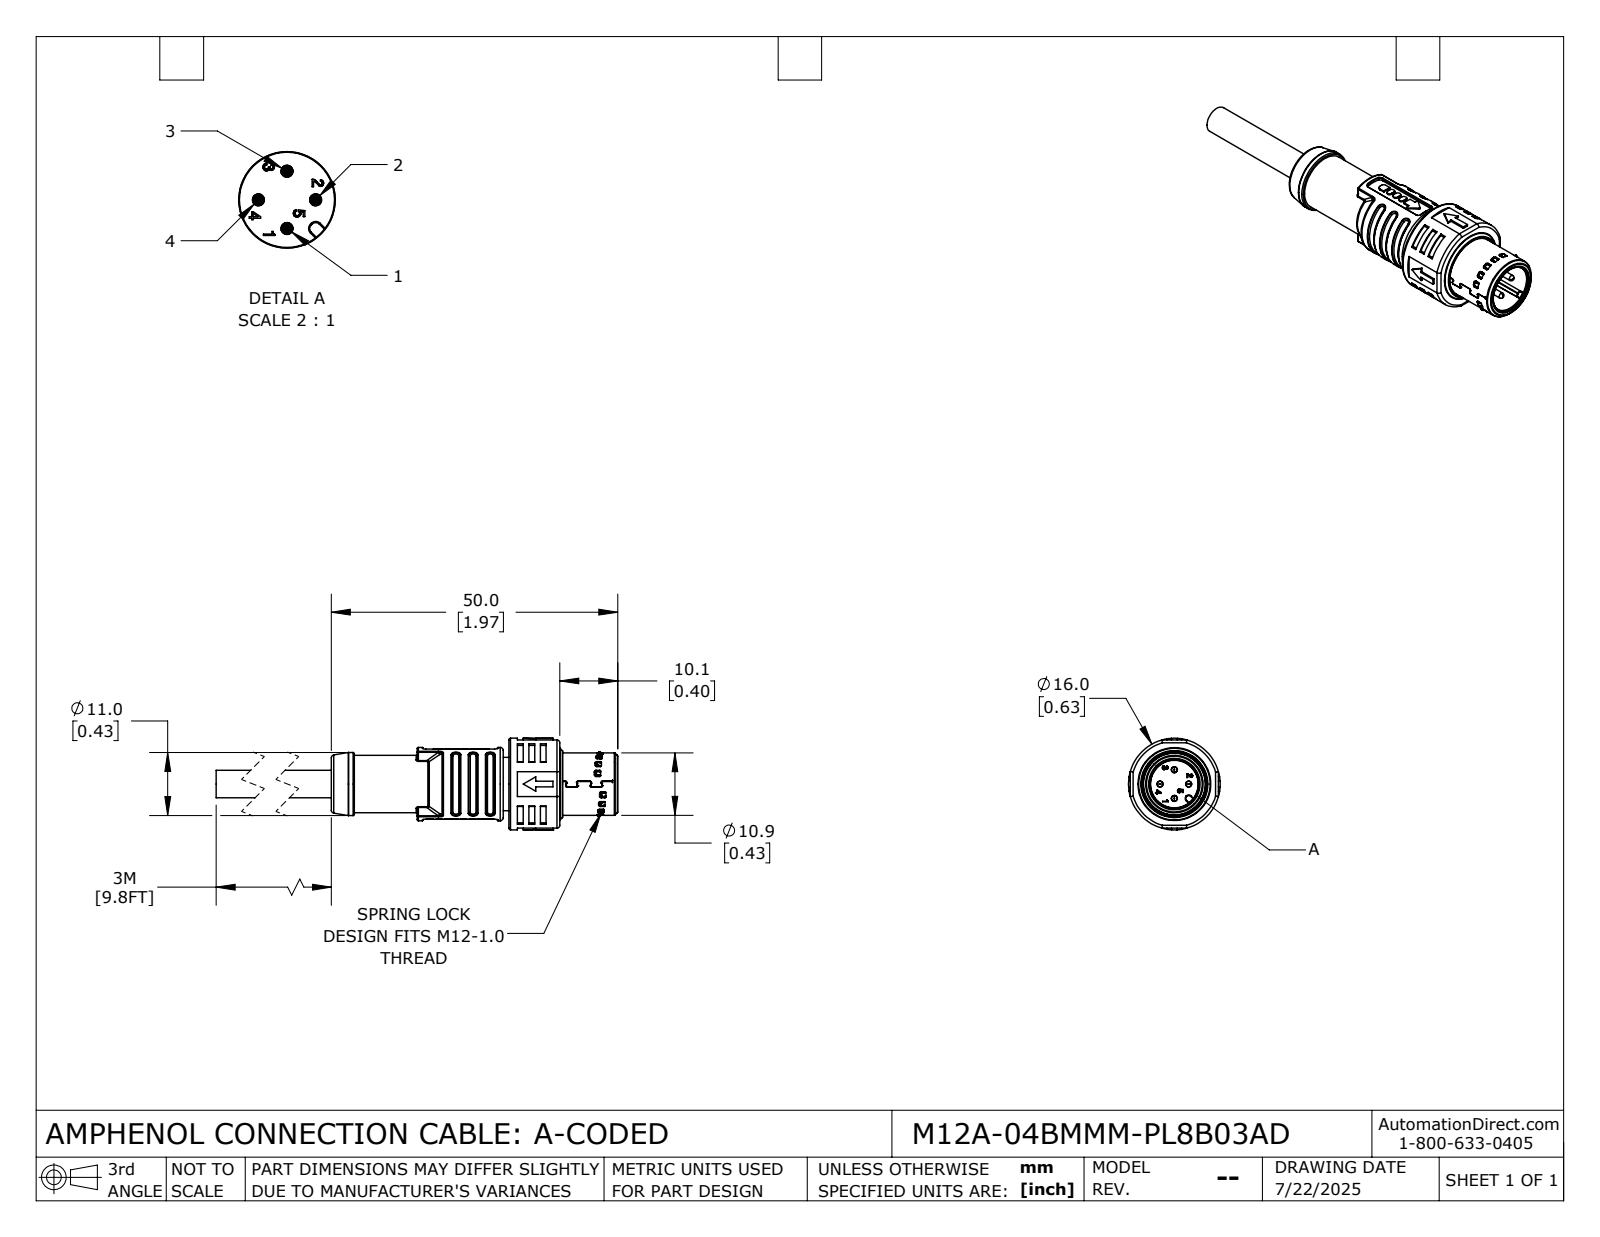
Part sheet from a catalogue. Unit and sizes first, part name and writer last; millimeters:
Units: millimetres
Overall size (bounding box): 72.7 × 16 × 16
Round holes (diameter × count): ⌀1 ×4, ⌀1.4 ×4, ⌀8.3 ×1, ⌀9 ×1, ⌀10.2 ×1, ⌀10.5 ×1, ⌀11.5 ×1, ⌀11.8 ×1, ⌀14.2 ×1
Round bosses / shafts (diameter × count): ⌀1.4 ×4, ⌀1 ×4, ⌀16 ×1, ⌀14.1 ×1, ⌀12.8 ×1, ⌀12.4 ×1, ⌀11 ×1, ⌀10.9 ×1
Partial cylindrical surfaces — rounded edges, fillets, slot ends (radius × count): R0.2 ×114, R0.3 ×66, R0.3 ×64, R0.2 ×44, R0.5 ×38, R0.1 ×12, R0.7 ×11, R0.1 ×10
Main face-to-face distances: 1, 10.1, 8.9, 8.6, 2.5, 1.5, 1.2, 32.5, 15.4, 41.1
Hole centre spacings: 2.5, 3.5, 5
Volume: 5 180 mm³ · Surface area: 5 970 mm²
Bodies: 1 solid, 2276 faces (1081 planar, 672 cylindrical, 523 other)
Part name (STEP PRODUCT): M12A-04BMMM-PL8B03AD
STEP written by: SolidWorks 2024 (CONFIG_CONTROL_DESIGN)
